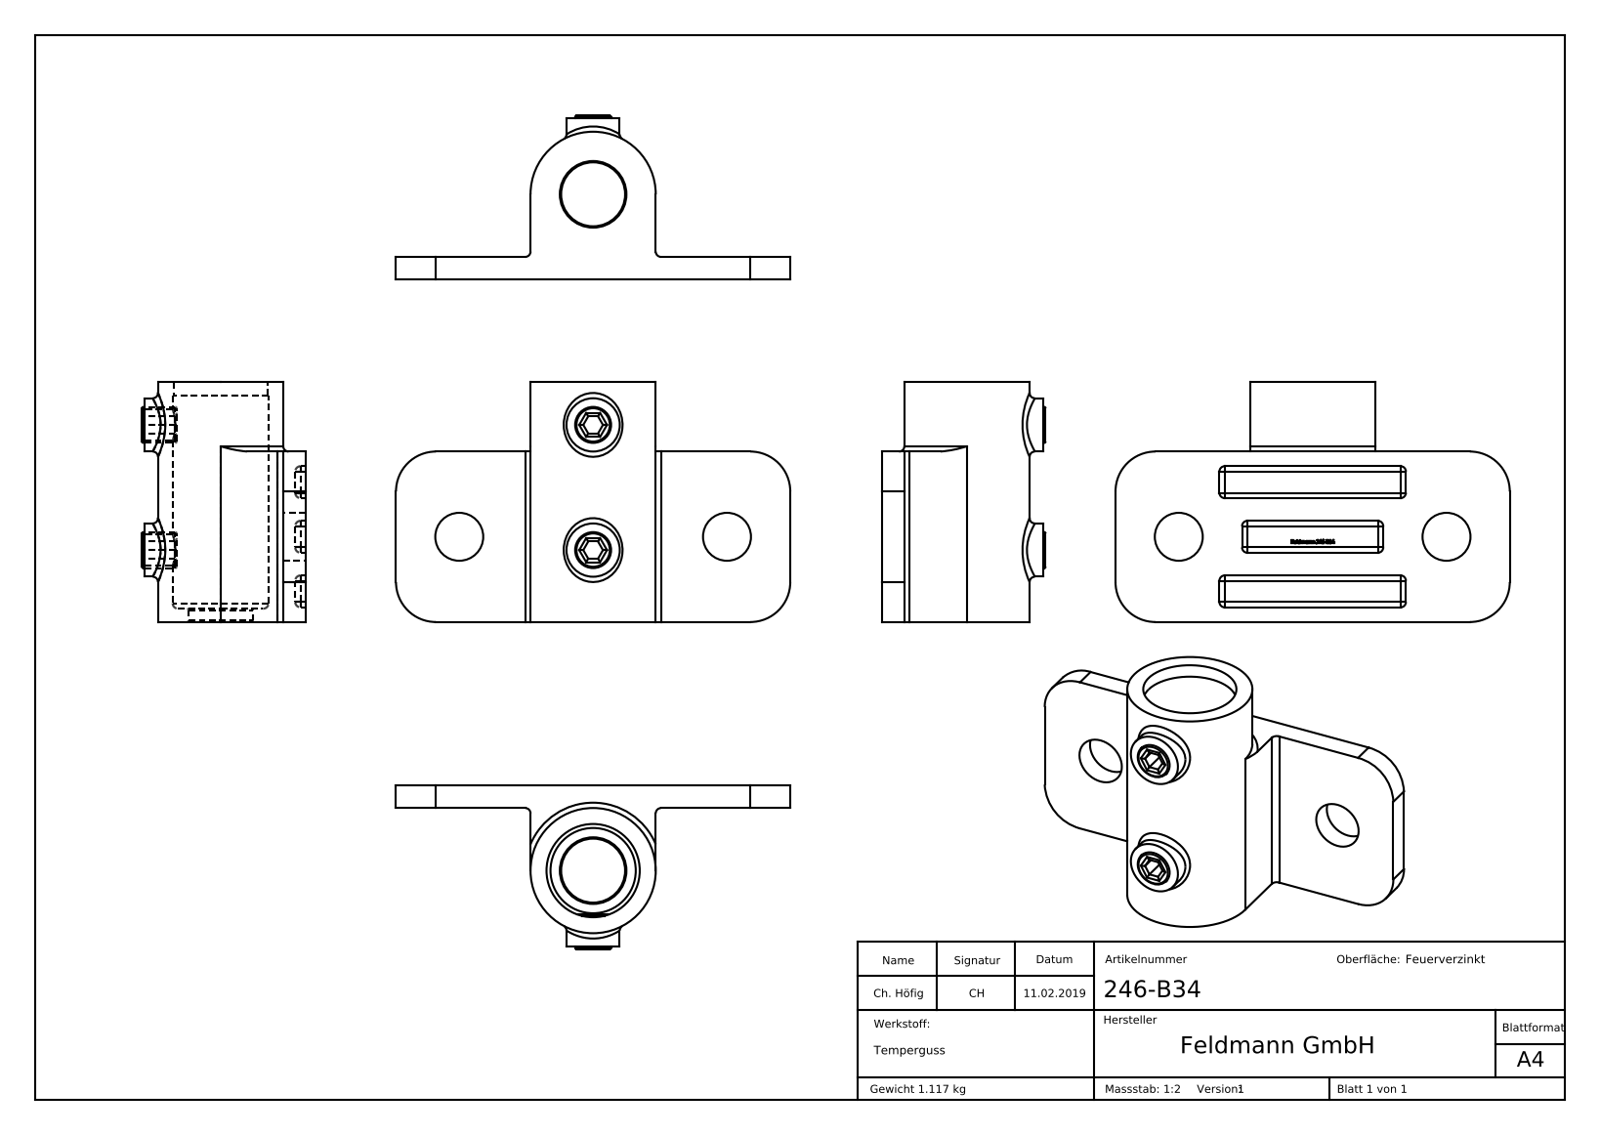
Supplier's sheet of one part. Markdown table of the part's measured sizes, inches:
| quantity | value |
| --- | --- |
| part name | 246-B34; 246-B34 Teil2; 246-XXX Teil1_246-B34 Teil1 |
| STEP written by | SolidWorks 2015 (CONFIG_CONTROL_DESIGN) |
| units | inches |
| bodies | 3 solids, 369 faces (173 planar, 78 cylindrical, 118 other) |
| overall size | 5.827 × 3.543 × 2.421 |
| volume | 9.321 in³ |
| surface area | 74.09 in² |
| round holes (diameter × count) | 0.465 × 2, 0.709 × 2, 0.945 × 1, 1.378 × 1, 1.417 × 1 |
| round bosses / shafts (diameter × count) | 0.787 × 2, 0.531 × 2, 1.85 × 1 |
| partial cylindrical surfaces (radius × count) | 0.079 × 48, 0.591 × 4 |
| main face-to-face distances | 0.335, 1.85, 0.177, 0.157, 2.52, 1.024, 3.543, 1.988, 3.839, 2.047 |
| hole center spacings | 1.988, 2.578, 1.85, 3.957 |
